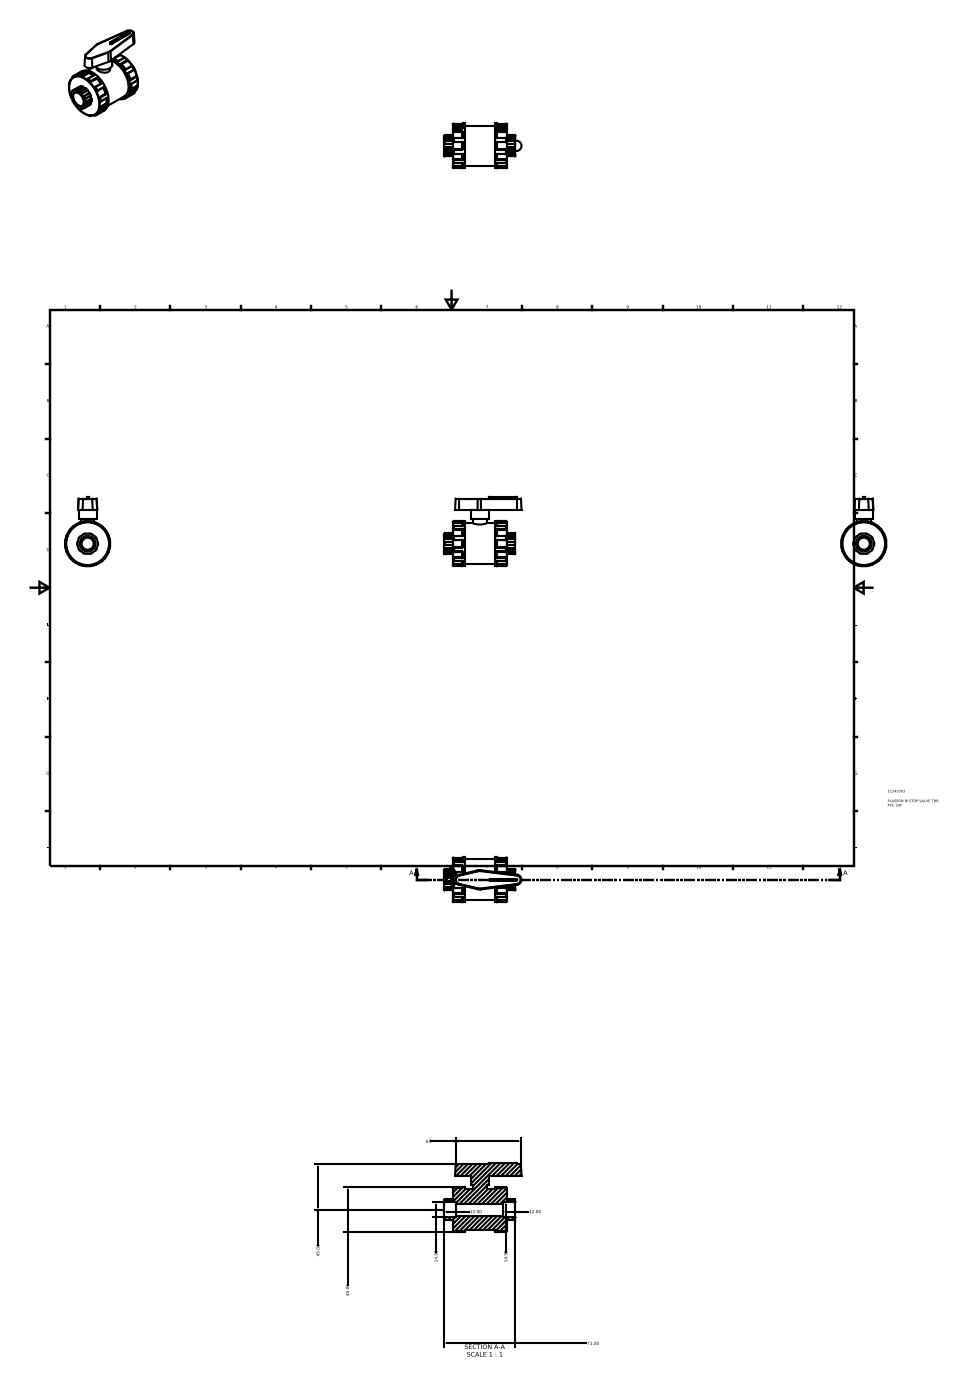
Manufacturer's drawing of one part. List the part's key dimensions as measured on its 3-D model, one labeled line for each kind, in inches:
Part name (STEP PRODUCT): 11241003
STEP written by: Autodesk Inventor 2015 (AUTOMOTIVE_DESIGN)
Units: inches
Bodies: 1 solid, 434 faces (114 planar, 192 cylindrical, 128 other)
Overall size (bounding box): 3.035 × 2.711 × 1.772
Volume: 5.149 in³ · Surface area: 29.22 in²
Round holes (diameter × count): ⌀0.471 ×1, ⌀0.589 ×1
Round bosses / shafts (diameter × count): ⌀1.772 ×1, ⌀1.701 ×1, ⌀1.594 ×1, ⌀0.709 ×1, ⌀0.531 ×1
Partial cylindrical surfaces — rounded edges, fillets, slot ends (radius × count): R0.018 ×64, R0.018 ×10, R0.012 ×4, R0.035 ×2, R0.394 ×1, R0.412 ×1
Main face-to-face distances: 2.134, 0.472, 0.443, 1.661, 0.331, 1.992, 1.189, 0.803, 2.465, 0.354
